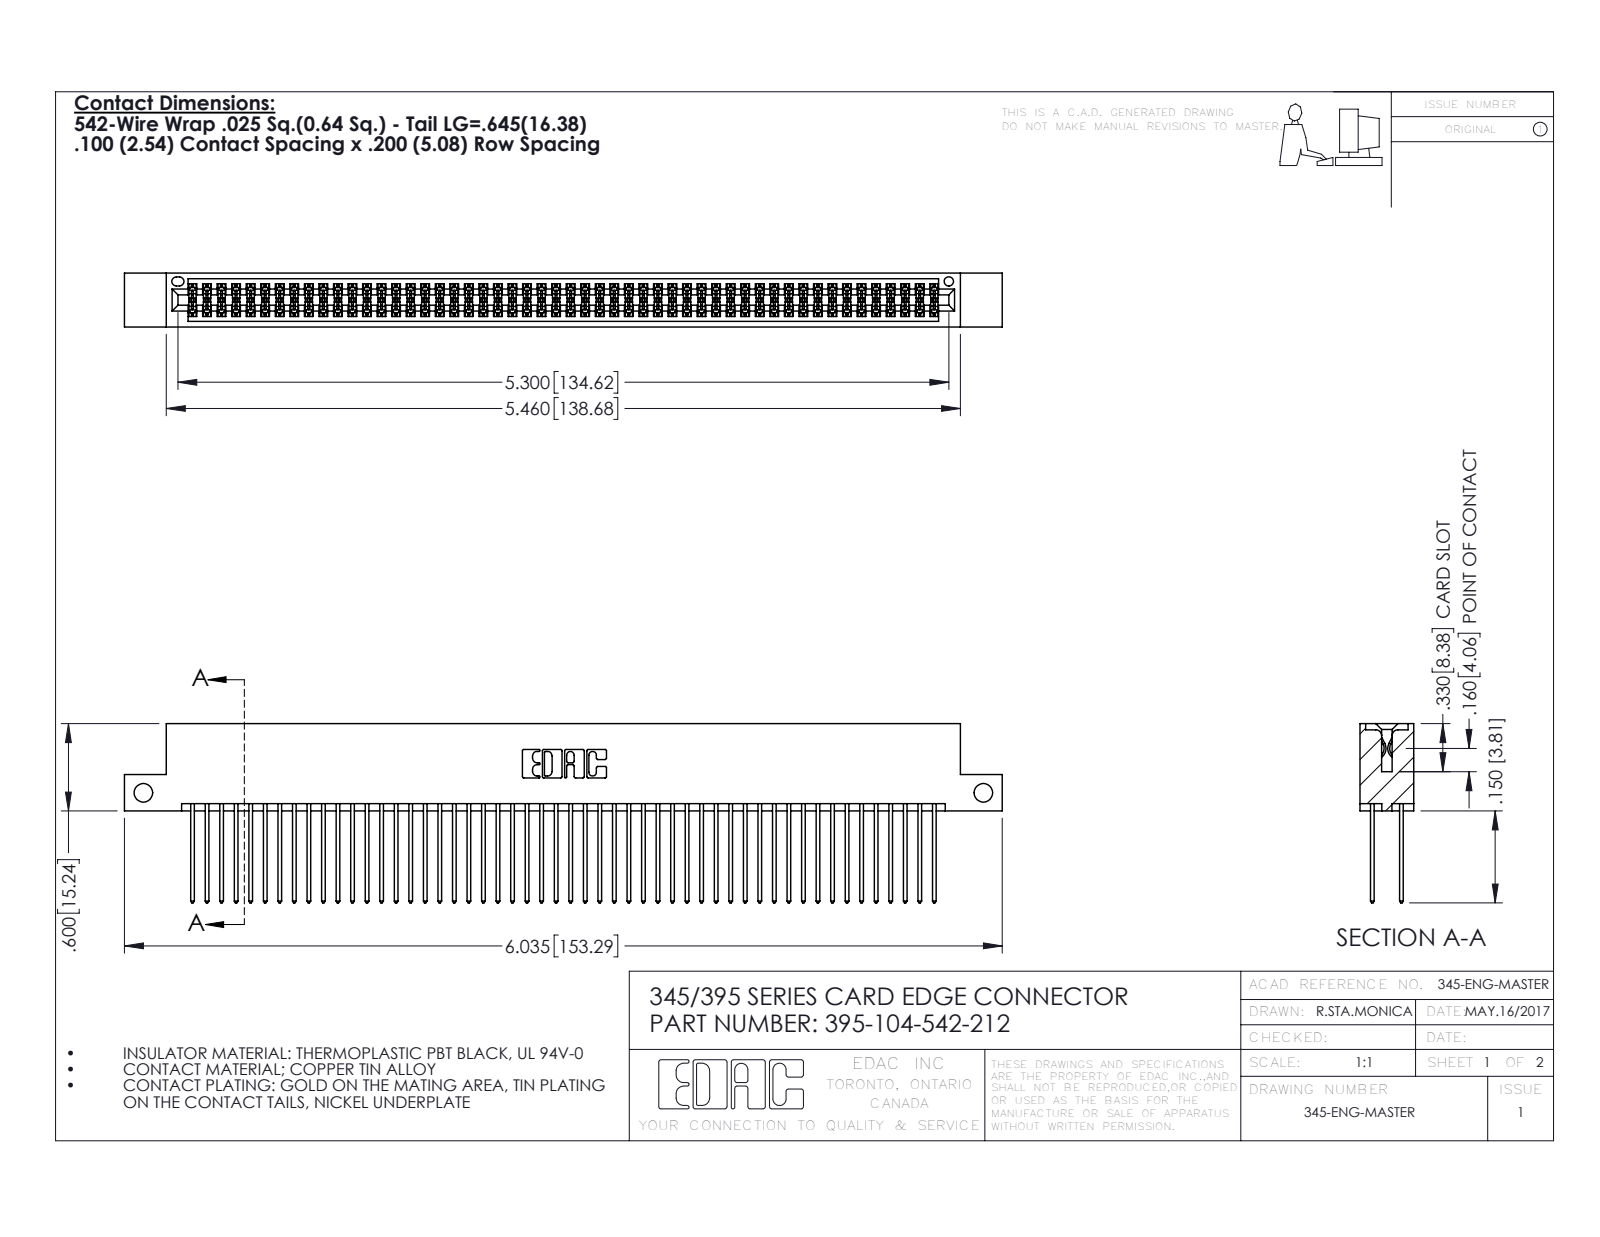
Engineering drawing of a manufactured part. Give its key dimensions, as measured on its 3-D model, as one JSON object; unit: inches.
{"part_name": "345 Part_Flush Mounting Lugs - Side Mount; 345-292-001_345-293-142; 395-104-542-212", "step_written_by": "SolidWorks 2016 (CONFIG_CONTROL_DESIGN)", "units": "inches", "bodies": {"solids": 105, "faces": 5326, "planar": 3512, "cylindrical": 1814, "other": 0}, "overall_size": [6.035, 1.232, 0.37], "volume_in3": 0.939, "surface_area_in2": 38.84, "round_holes": [[0.128, 2], [0.064, 1]], "partial_cylinders_radius": [[0.006, 156], [0.01, 104], [0.01, 22], [0.007, 6], [0.031, 6], [0.026, 3], [0.014, 2], [0.019, 2]], "face_to_face_distances": [0.298, 0.072, 0.2, 0.098, 0.272, 0.025, 0.225, 0.37, 0.175, 0.149], "hole_center_spacings": [5.775]}
